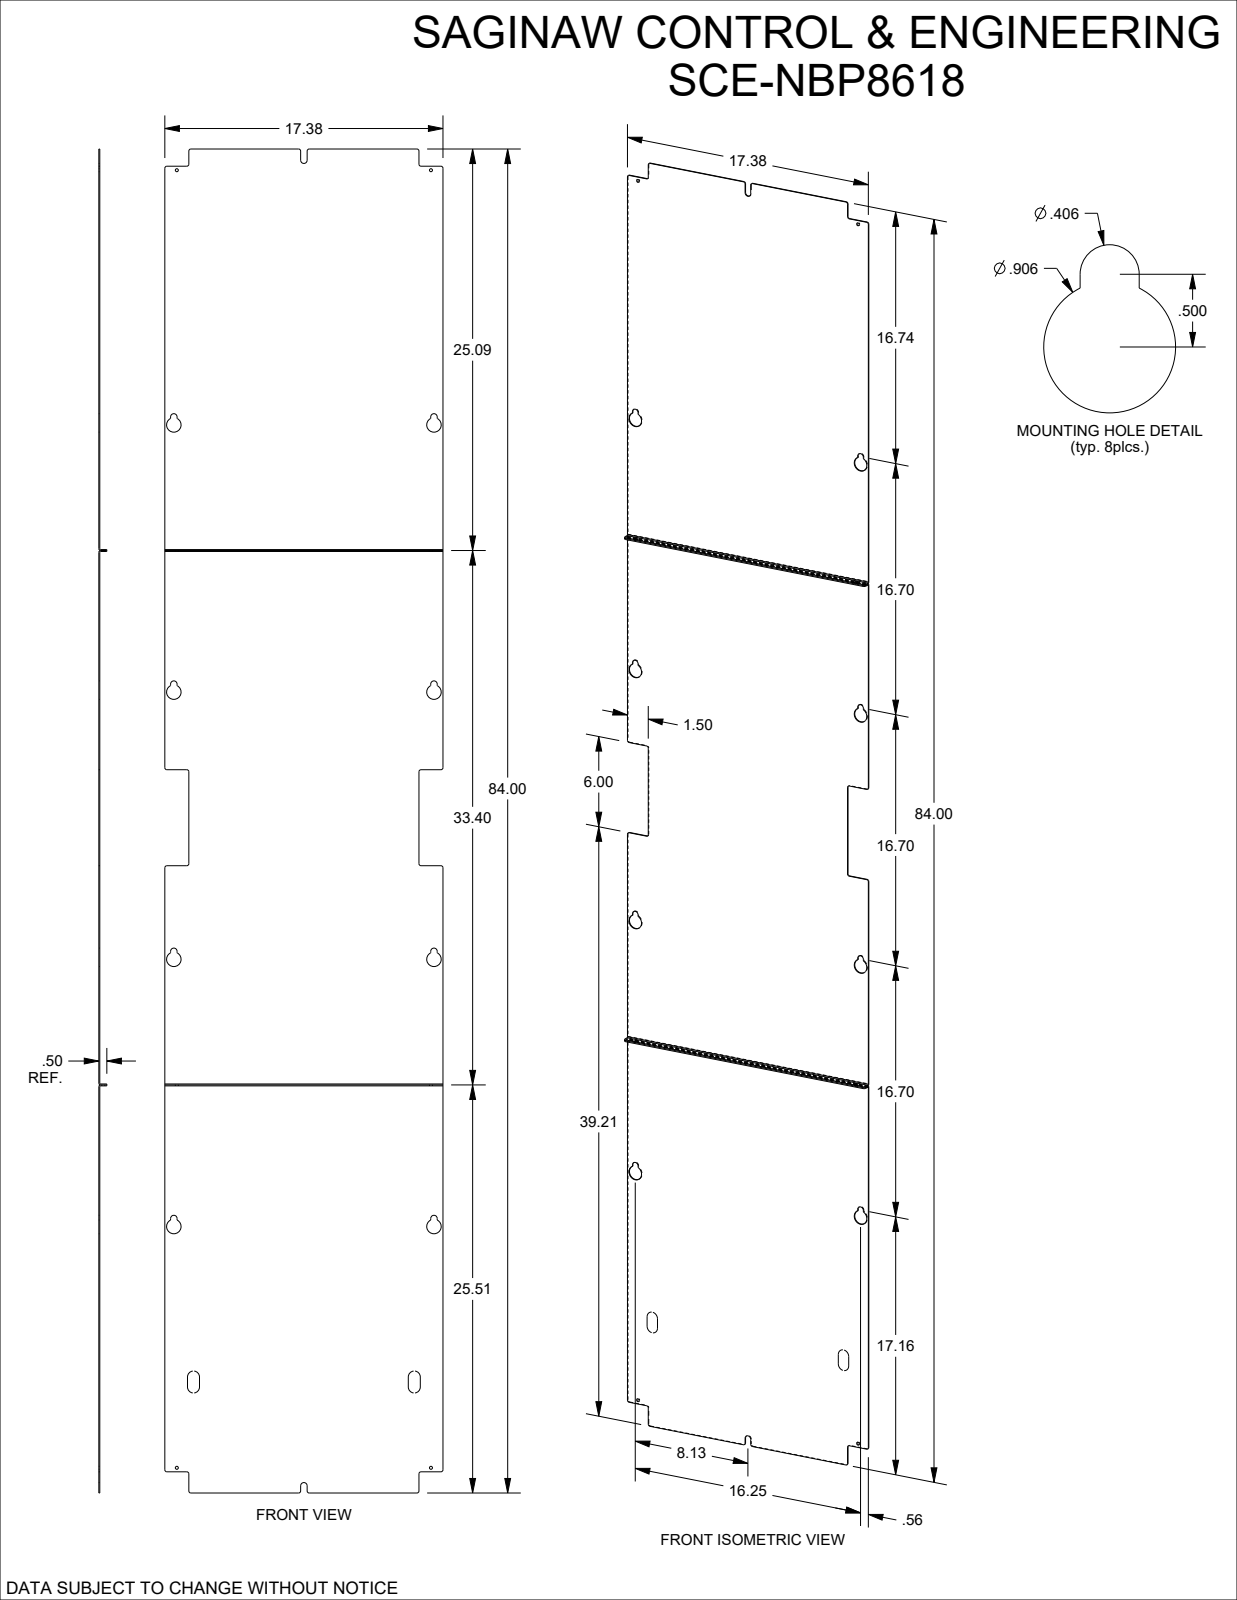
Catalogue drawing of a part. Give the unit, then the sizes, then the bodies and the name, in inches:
Units: inches
Overall size (bounding box): 84 × 17.375 × 0.5
Round holes (diameter × count): ⌀0.906 ×8, ⌀0.188 ×6
Partial cylindrical surfaces — rounded edges, fillets, slot ends (radius × count): R0.125 ×26, R0.03 ×12, R0.203 ×10, R0.052 ×4, R0.112 ×4
Main face-to-face distances: 0.06, 33.4, 0.12, 33.46, 33.34, 33.52, 33.28, 17.375, 0.44, 0.5
Hole centre spacings: 16.7, 23.302, 16.25, 33.4, 37.143, 15.875, 15.081, 15.921
Volume: 87.33 in³ · Surface area: 2 930 in²
Bodies: 3 solids, 174 faces (80 planar, 94 cylindrical, 0 other)
Part name (STEP PRODUCT): SCE-NBP8618
STEP written by: SolidWorks 2023 (AUTOMOTIVE_DESIGN)
